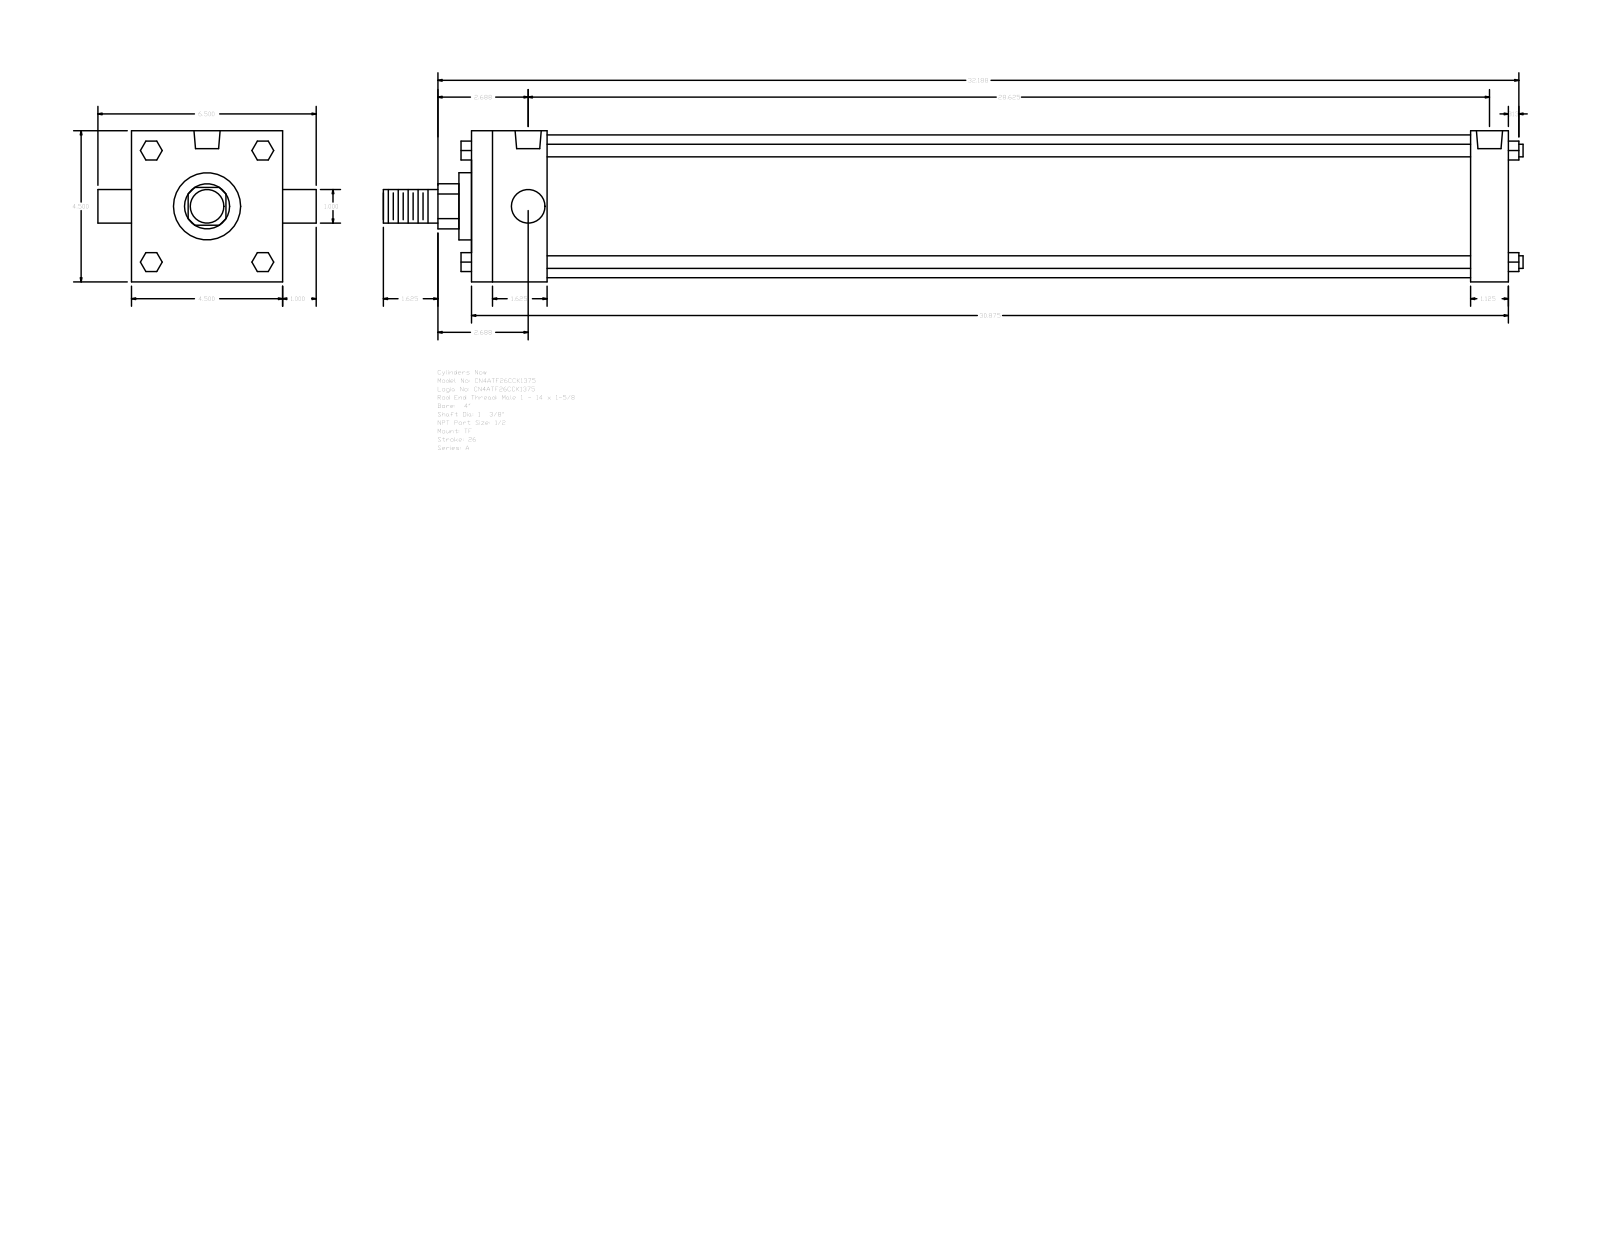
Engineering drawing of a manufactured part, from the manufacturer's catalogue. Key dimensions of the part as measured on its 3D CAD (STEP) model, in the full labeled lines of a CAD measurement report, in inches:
Part name (STEP PRODUCT): A_TF__0400_1.375
STEP written by: GSSL Pune (CONFIG_CONTROL_DESIGN)
Units: inches
Bodies: 0 solids, 120 faces (92 planar, 28 cylindrical, 0 other)
Overall size (bounding box): 33.937 × 6.5 × 4.5
Round holes (diameter × count): ⌀0.344 ×3, ⌀0.778 ×2
Round bosses / shafts (diameter × count): ⌀0.375 ×4, ⌀1 ×2, ⌀4.25 ×1, ⌀2 ×1, ⌀1.375 ×1
Partial cylindrical surfaces — rounded edges, fillets, slot ends (radius × count): R0.672 ×1
Main face-to-face distances: 4.5, 30.875, 2.25, 29.75, 1.125, 27.5, 28.625, 2.625, 0.563, 1
Hole centre spacings: 0.125, 28.5, 28.375, 28.625
